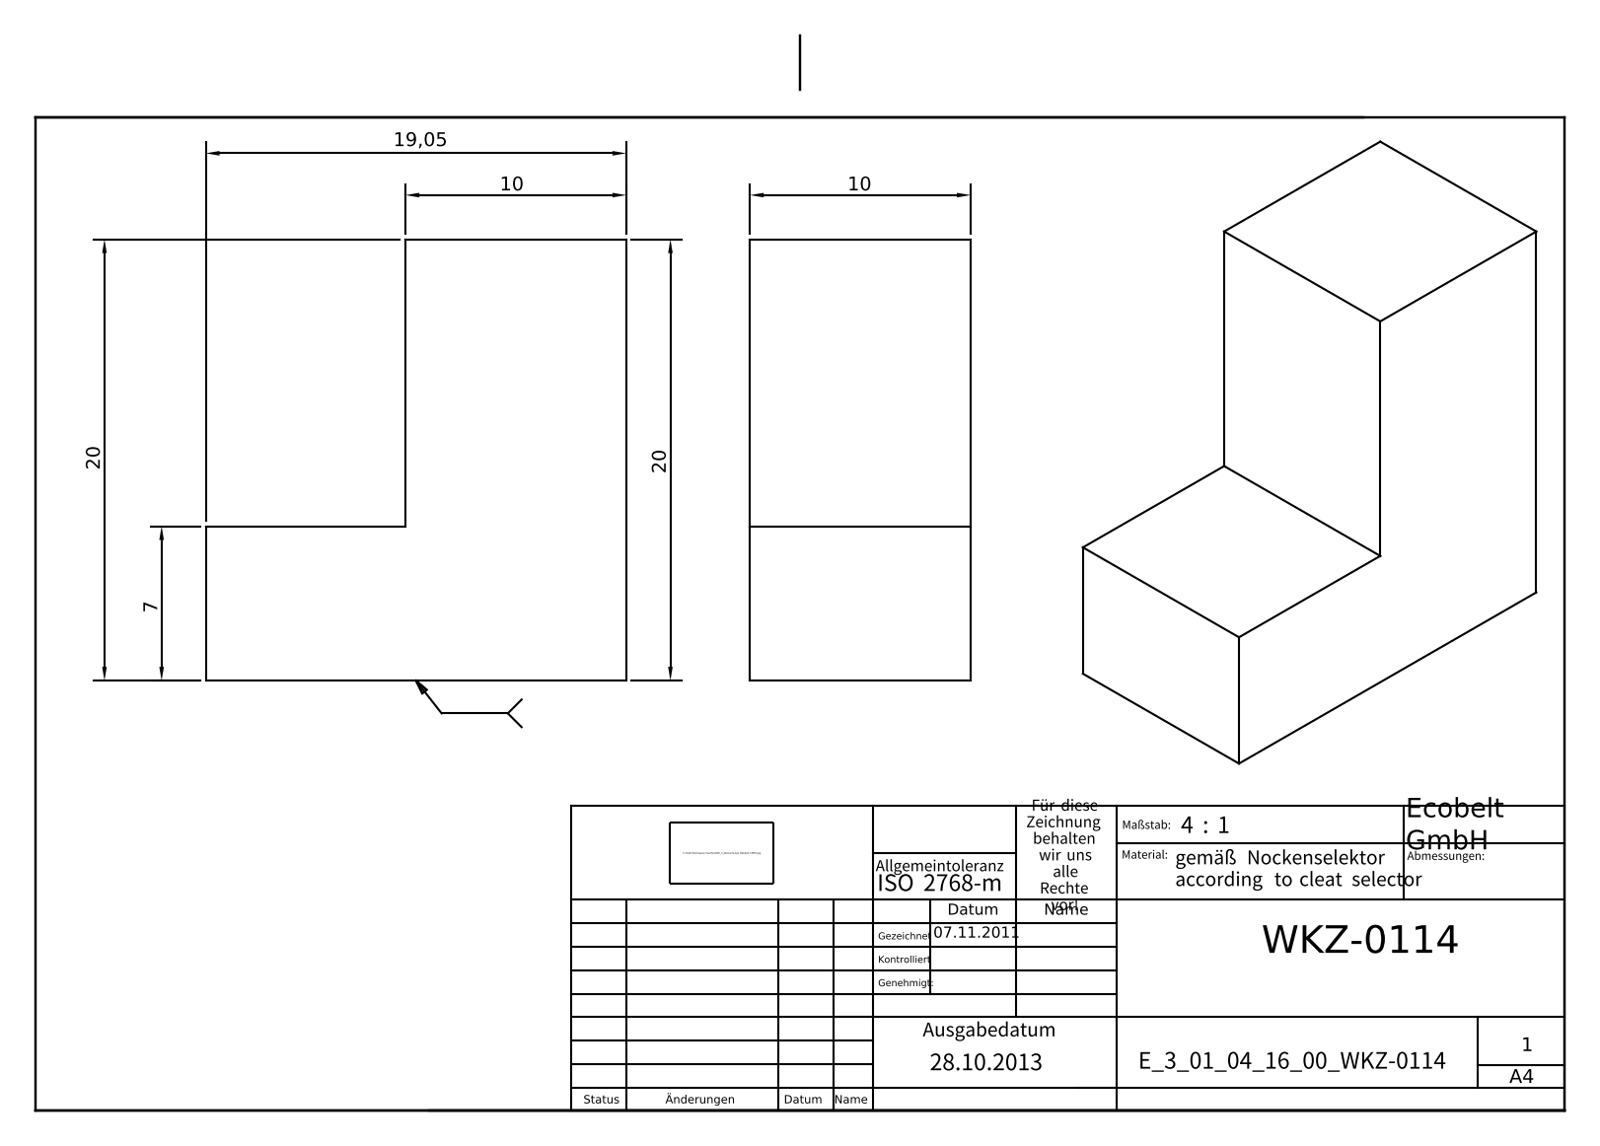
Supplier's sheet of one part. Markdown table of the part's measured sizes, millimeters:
| quantity | value |
| --- | --- |
| part name | E_3_01_04_16_00_WKZ-0114 |
| STEP written by | Autodesk Inventor 2025 (AUTOMOTIVE_DESIGN) |
| units | millimeters |
| bodies | 1 solid, 8 faces (8 planar, 0 cylindrical, 0 other) |
| overall size | 20 × 19.05 × 10 |
| volume | 2 634 mm³ |
| surface area | 1 308 mm² |
| main face-to-face distances | 10, 20, 7, 13, 9.05, 19.05 |
